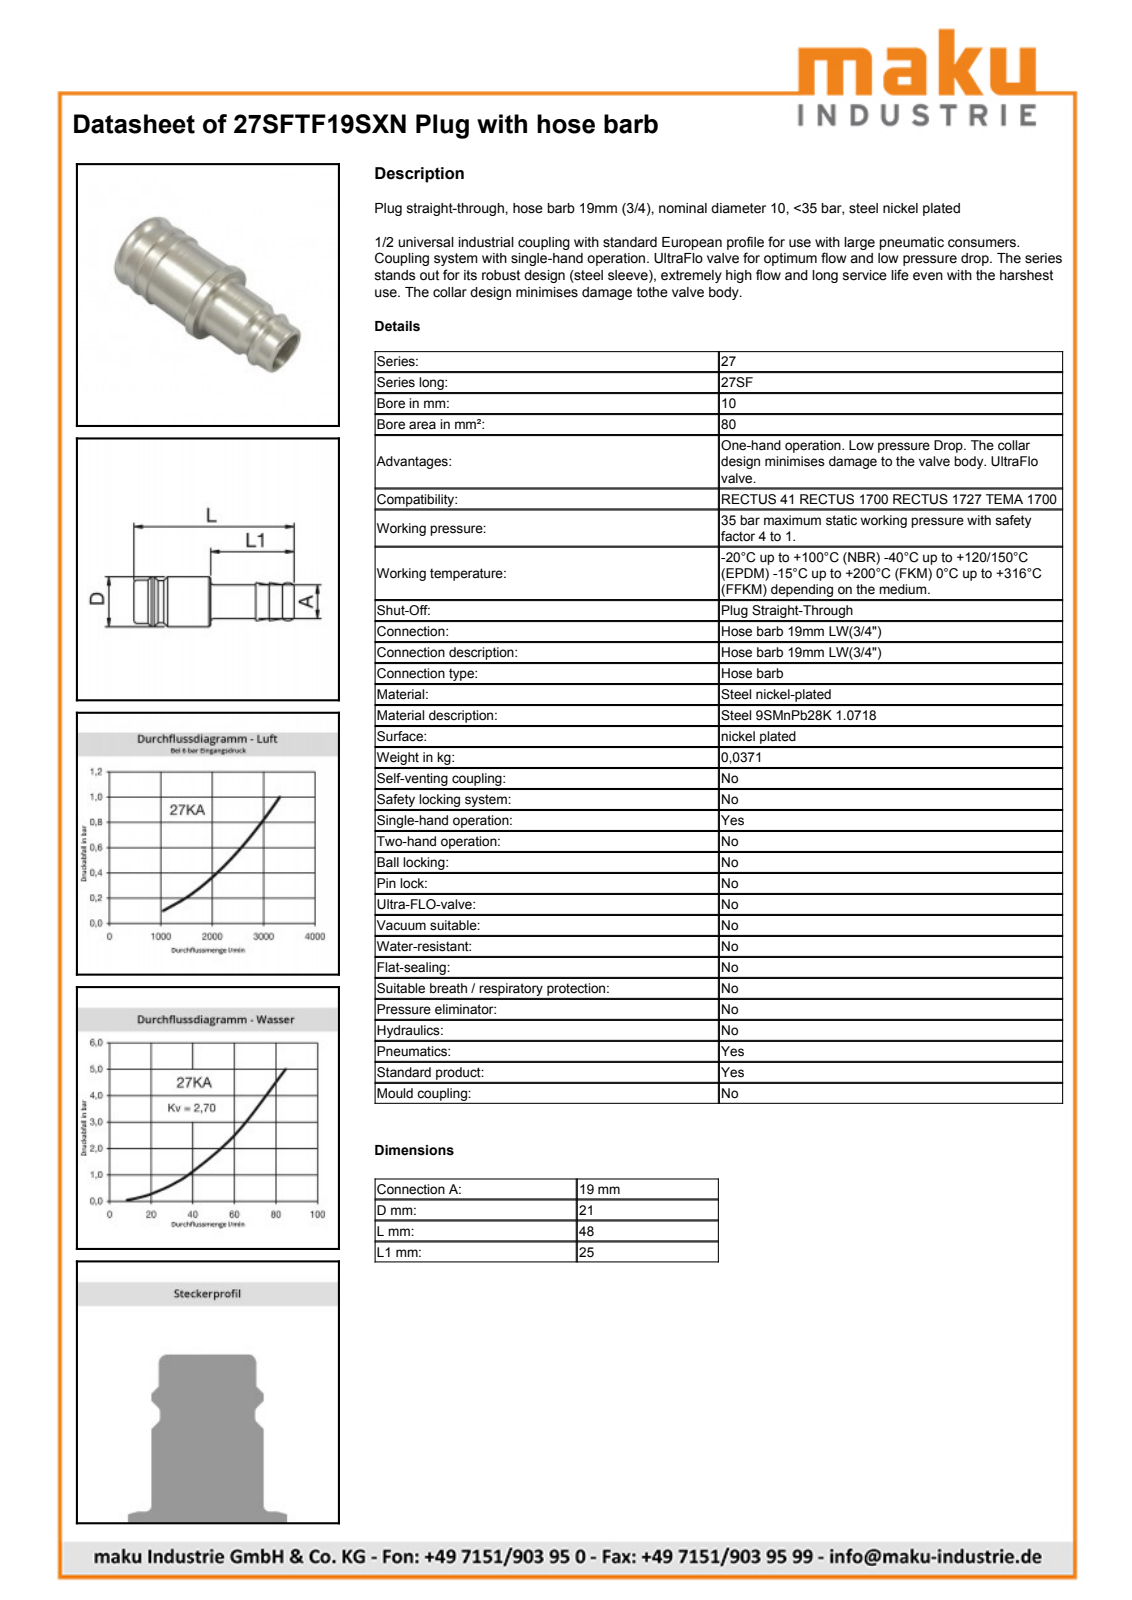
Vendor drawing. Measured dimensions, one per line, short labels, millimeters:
name: D102858
written by: Autodesk Inventor 2011 (AUTOMOTIVE_DESIGN)
unit: mm
bodies: 1 solid, 25 faces (4 planar, 6 cylindrical, 15 other)
size: 49 × 21 × 21
volume: 11 764 mm³; area: 3 364 mm²
bosses: 1× ⌀21, 1× ⌀19.1, 1× ⌀15, 1× ⌀13, 1× ⌀12.65
face distances: 27.5, 21.5, 49, 37.5, 16, 11.5
